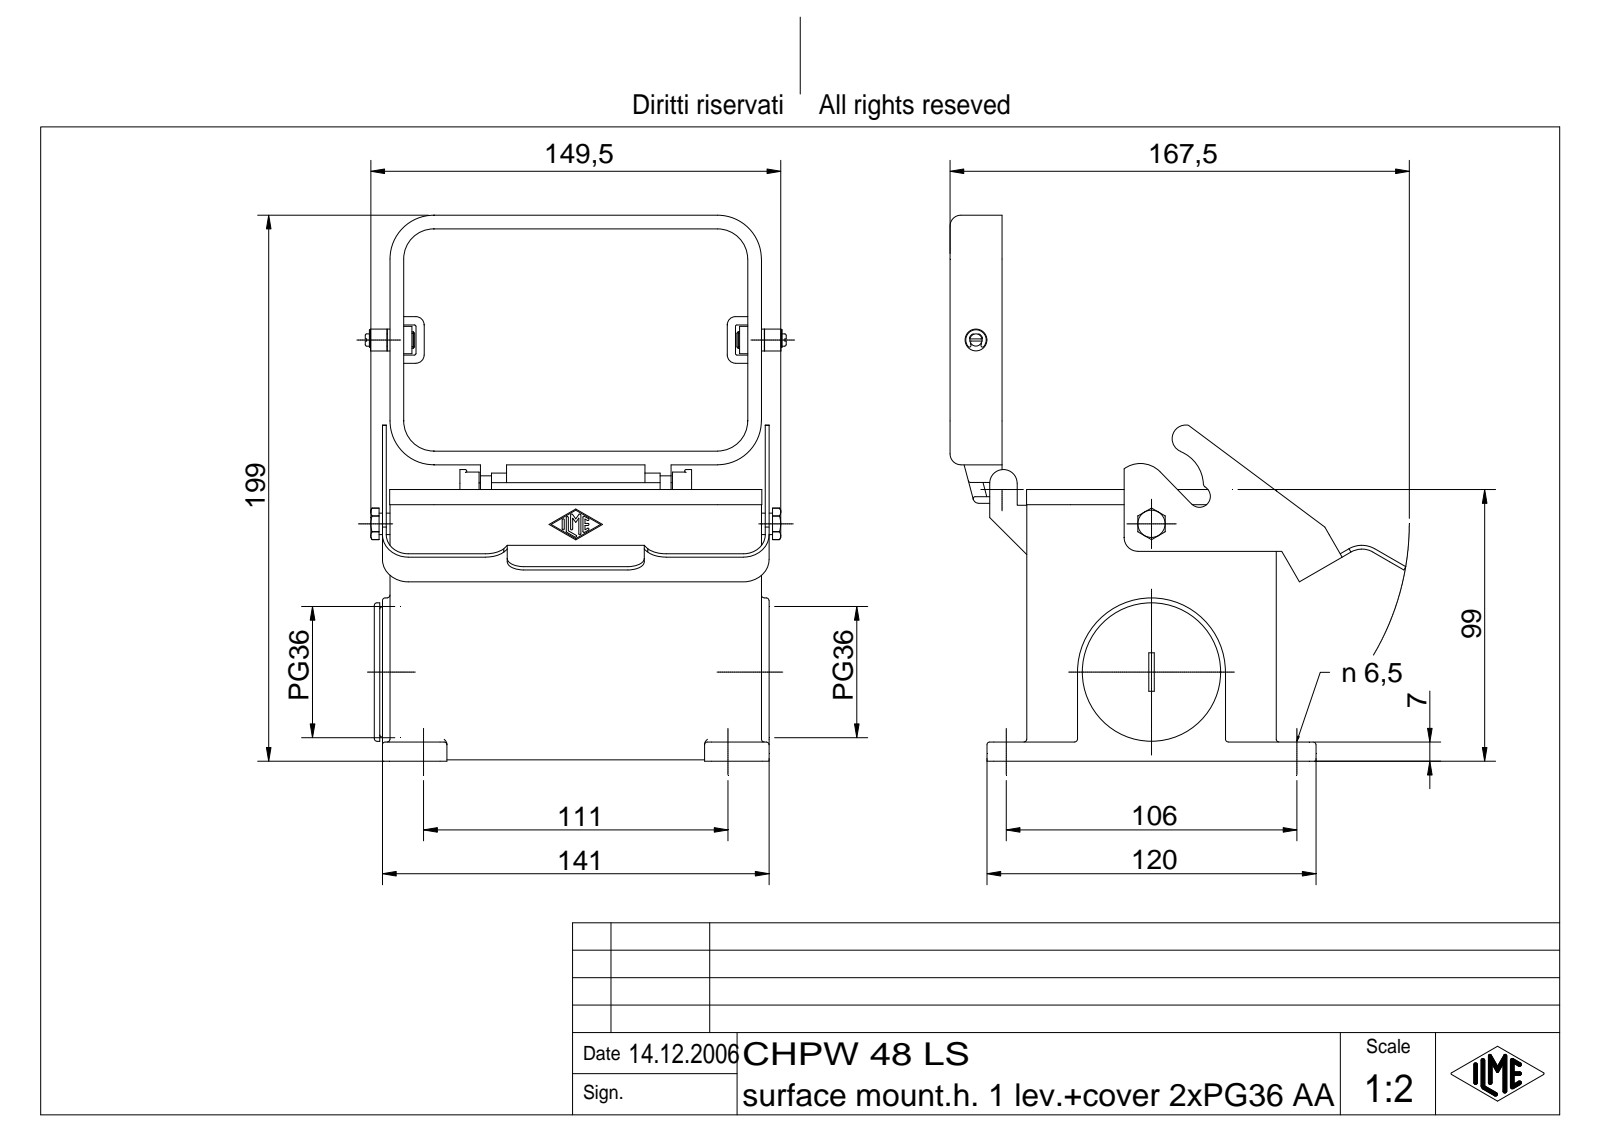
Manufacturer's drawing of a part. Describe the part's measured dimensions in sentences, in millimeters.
The part is named "CHPW 48 LS". Its 3-D file was written by "Autodesk Inventor 7 (AUTOMOTIVE_DESIGN)". It is 8 solids with 813 faces: 202 planar, 291 cylindrical and 320 other. Overall it measures 199 by 166.2 by 153.5 millimeters. Its volume is 463 454 cubic millimeters and its surface area 178 153 square millimeters. Round holes: 4 of diameter 2.46, 4 of diameter 3.1, 2 of diameter 6.5, 1 of diameter 5.95, 1 of diameter 6, 1 of diameter 8, 1 of diameter 38.48, 1 of diameter 42.48, 1 of diameter 45.48. Round bosses or shafts: 1 of diameter 50.48, 1 of diameter 8, 1 of diameter 7.8, 1 of diameter 6.2, 1 of diameter 6, 1 of diameter 5, 1 of diameter 4.5, 1 of diameter 3.5. Partial cylindrical surfaces (rounded edges, fillets, slot ends): 37 of radius 1, 14 of radius 0.38, 13 of radius 0.5, 8 of radius 11, 8 of radius 16, 6 of radius 3, 5 of radius 2.5, 5 of radius 4. The main face-to-face distances are 5, 86, 114, 28, 91, 81, 119, 23, 33, 109. The hole center spacings are 27, 104, 107.45, 22.28, 49.12, 54, 57.11, 84.07.
